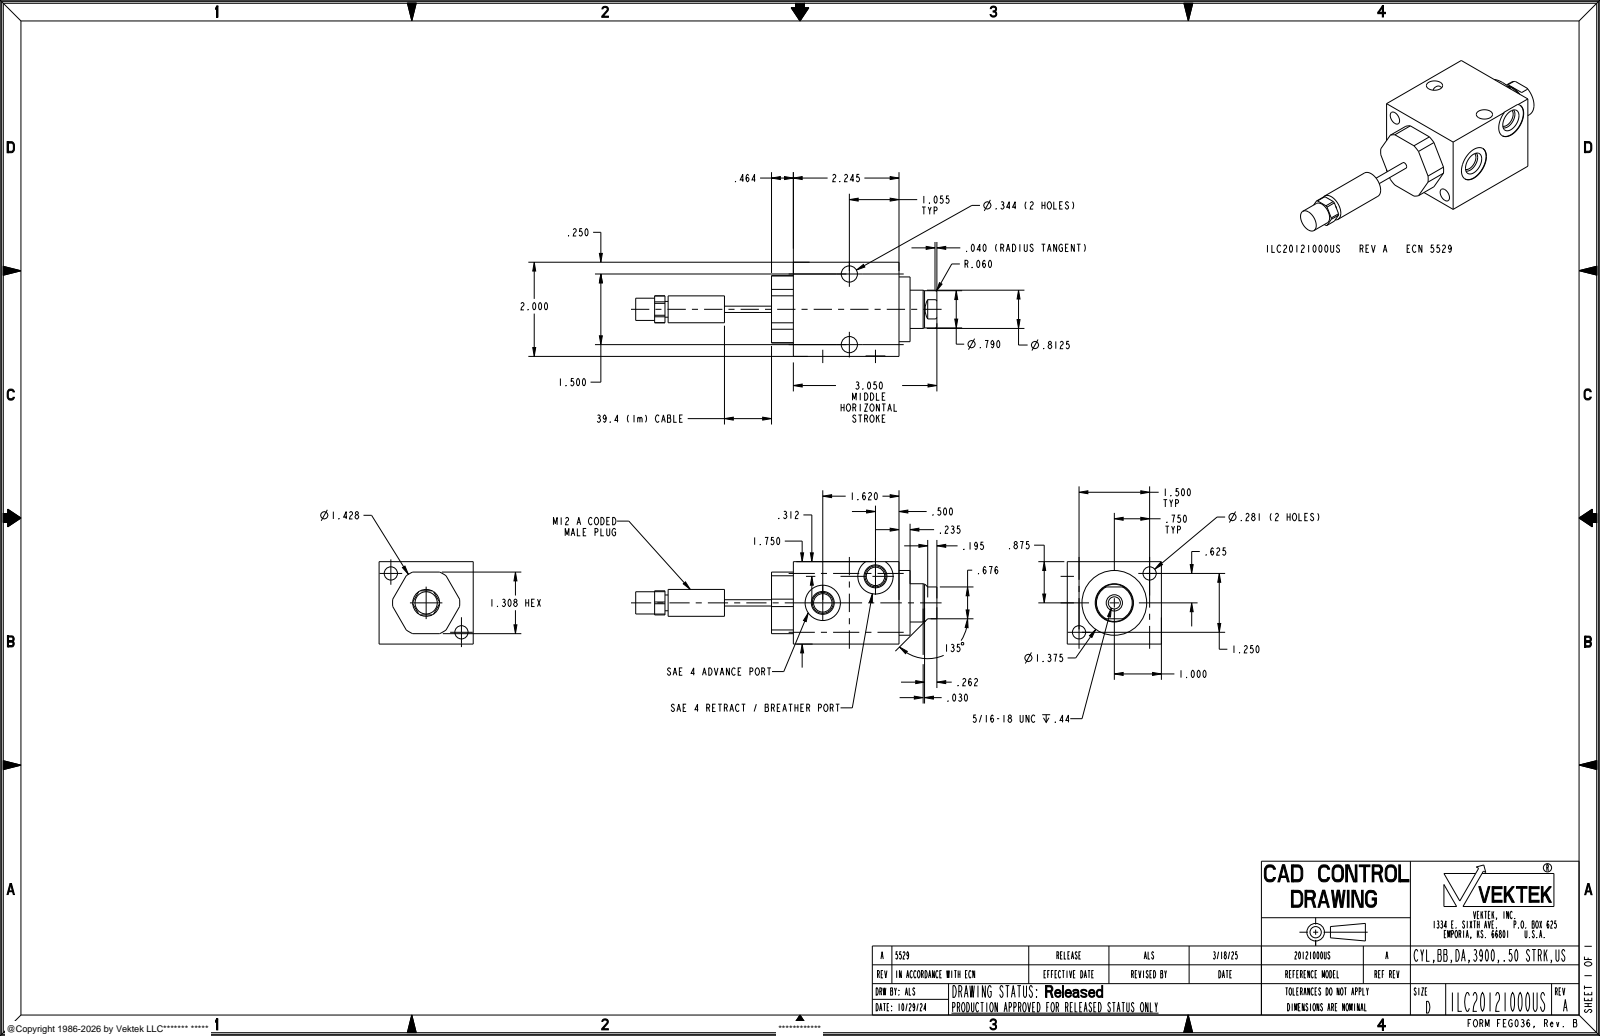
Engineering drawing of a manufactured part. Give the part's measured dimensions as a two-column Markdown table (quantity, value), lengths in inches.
| quantity | value |
| --- | --- |
| part name | ILC20121000US |
| STEP written by | CREO PARAMETRIC BY PTC INC, 2021164 (AUTOMOTIVE_DESIGN) |
| units | inches |
| bodies | 1 solid, 99 faces (36 planar, 49 cylindrical, 14 other) |
| overall size | 6.4 × 2.25 × 1.75 |
| volume | 8.86 in³ |
| surface area | 41.27 in² |
| round holes (diameter × count) | 0.281 × 2, 0.344 × 2, 0.392 × 2, 0.75 × 2, 0.257 × 1 |
| round bosses / shafts (diameter × count) | 1.375 × 1, 0.813 × 1, 0.79 × 1, 0.571 × 1, 0.472 × 1, 0.335 × 1, 0.312 × 1, 0.134 × 1 |
| partial cylindrical surfaces (radius × count) | 0.714 × 1 |
| main face-to-face distances | 1.75, 2, 2.245, 2.709, 0.464, 0.235, 2.48, 2.944, 1.308, 0.221 |
| hole center spacings | 0.976, 1.254, 1.5, 1.953 |
